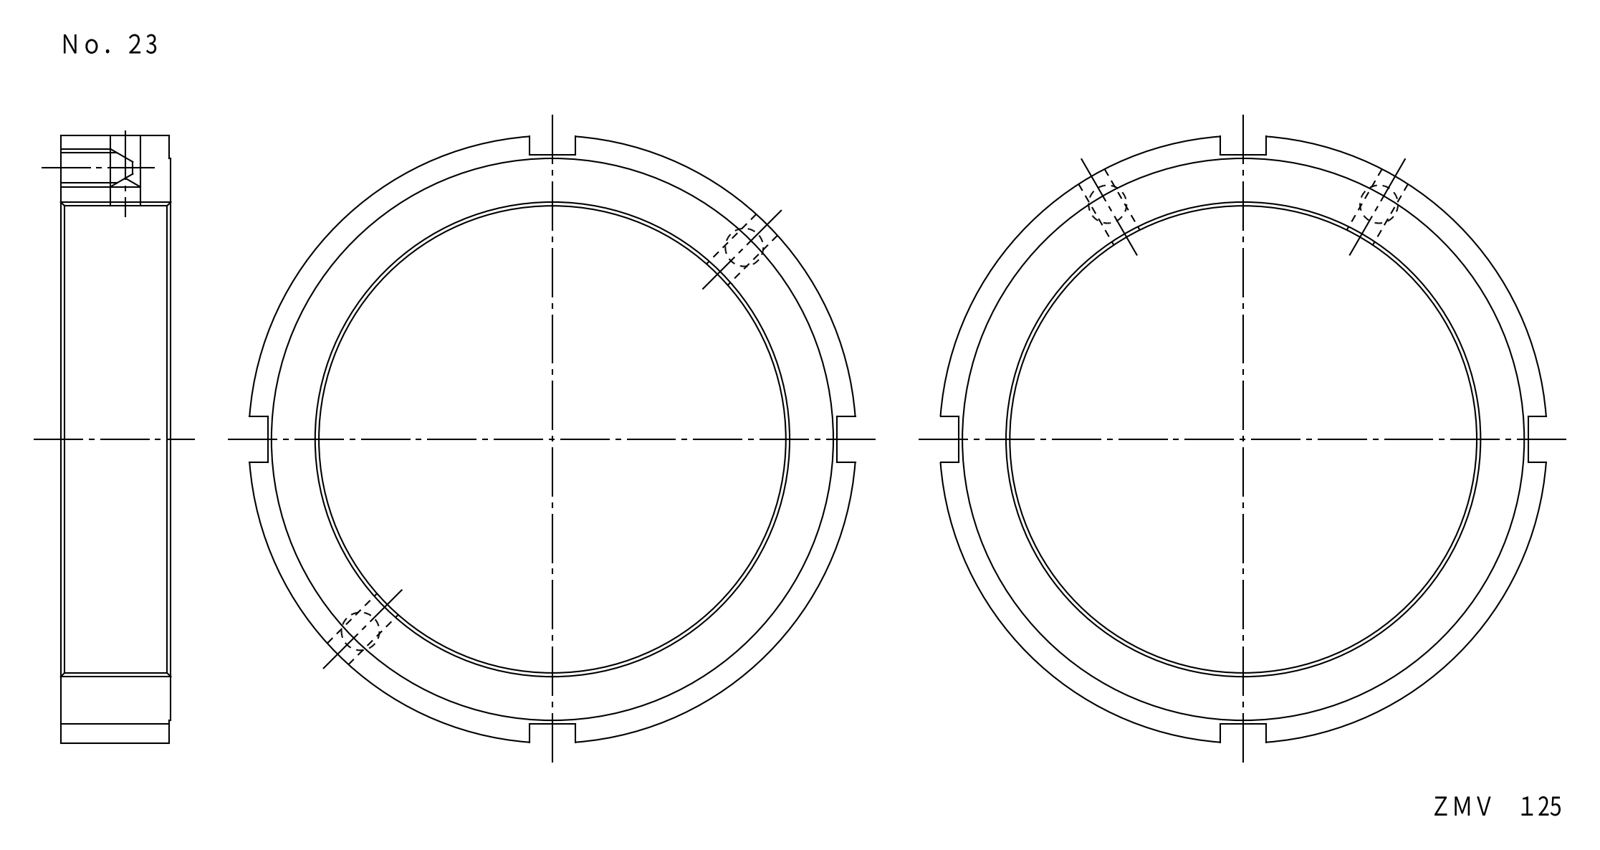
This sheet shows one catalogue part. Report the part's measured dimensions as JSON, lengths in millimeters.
{"part_name": "FKD ZMV125", "step_written_by": "Autodesk Inventor LT (CONFIG_CONTROL_DESIGN)", "units": "millimeters", "bodies": {"solids": 1, "faces": 29, "planar": 15, "cylindrical": 10, "other": 4}, "overall_size": [159.55, 159.55, 29], "volume_mm3": 215778, "surface_area_mm2": 43425, "round_holes": [[7.9, 2], [8.38, 2], [125, 1]], "round_bosses_or_shafts": [[160, 1], [148, 1]], "face_to_face_distances": [29, 0.5, 28.5, 69, 81, 150, 12], "hole_center_spacings": [71.5, 143.01]}
